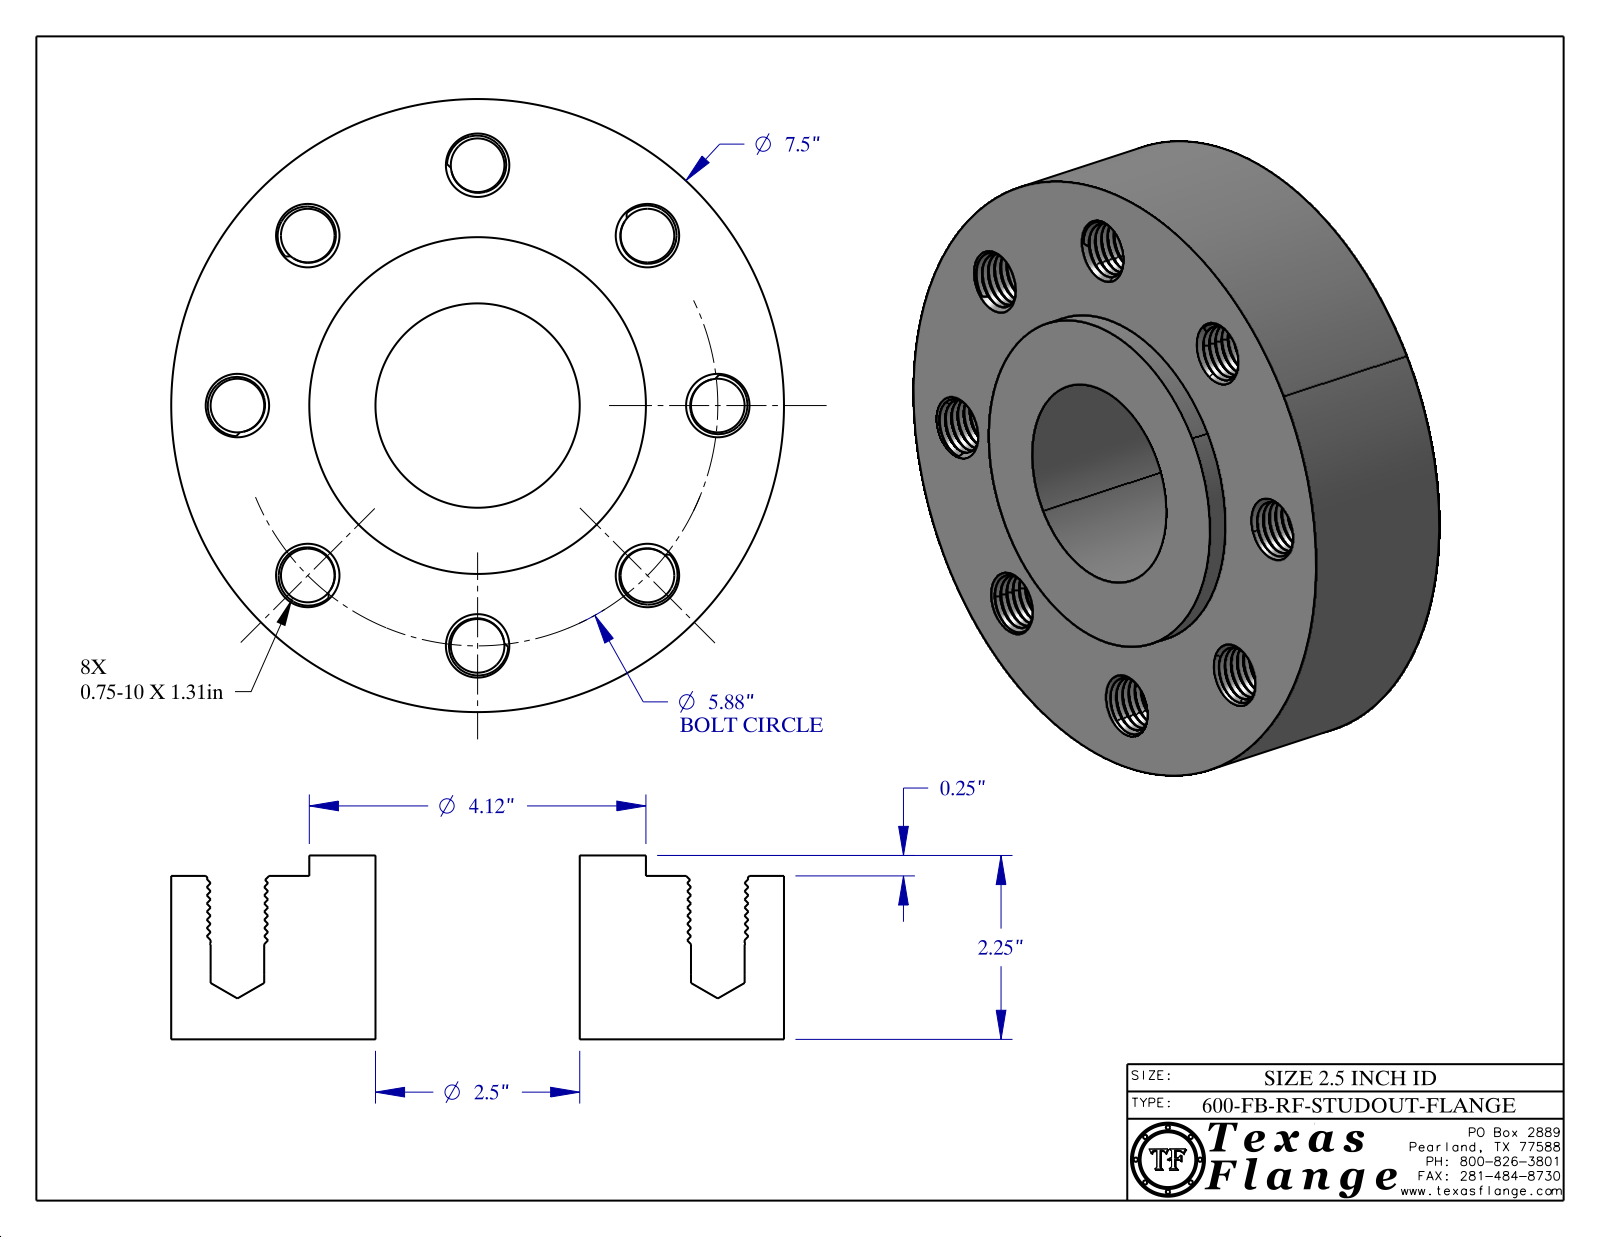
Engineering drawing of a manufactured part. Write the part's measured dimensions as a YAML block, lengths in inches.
part_name: "2.5-600-FB-RF-STUDOUT-FLANGE"
step_written_by: "CATIA V5 STEP AP214 (AUTOMOTIVE_DESIGN)"
units: inches
bodies: {solids: 1, faces: 874, planar: 368, cylindrical: 186, other: 320}
overall_size: [7.5, 7.5, 2.25]
volume: 76.58
surface_area: 174.3
round_holes:
  - {diameter: 0.656, count: 8}
  - {diameter: 1, count: 1}
  - {diameter: 2.5, count: 1}
round_bosses_or_shafts:
  - {diameter: 0.061, count: 8}
  - {diameter: 7.5, count: 1}
  - {diameter: 4.12, count: 1}
  - {diameter: 0.788, count: 1}
face_to_face_distances: [2, 0.25, 2.25, 0.015, 2.235, 1.985, 0.298, 0.292, 0.054, 0.248]
hole_center_spacings: [2.25, 5.432, 2.94, 2.94, 4.157, 4.158, 5.88, 5.88]
